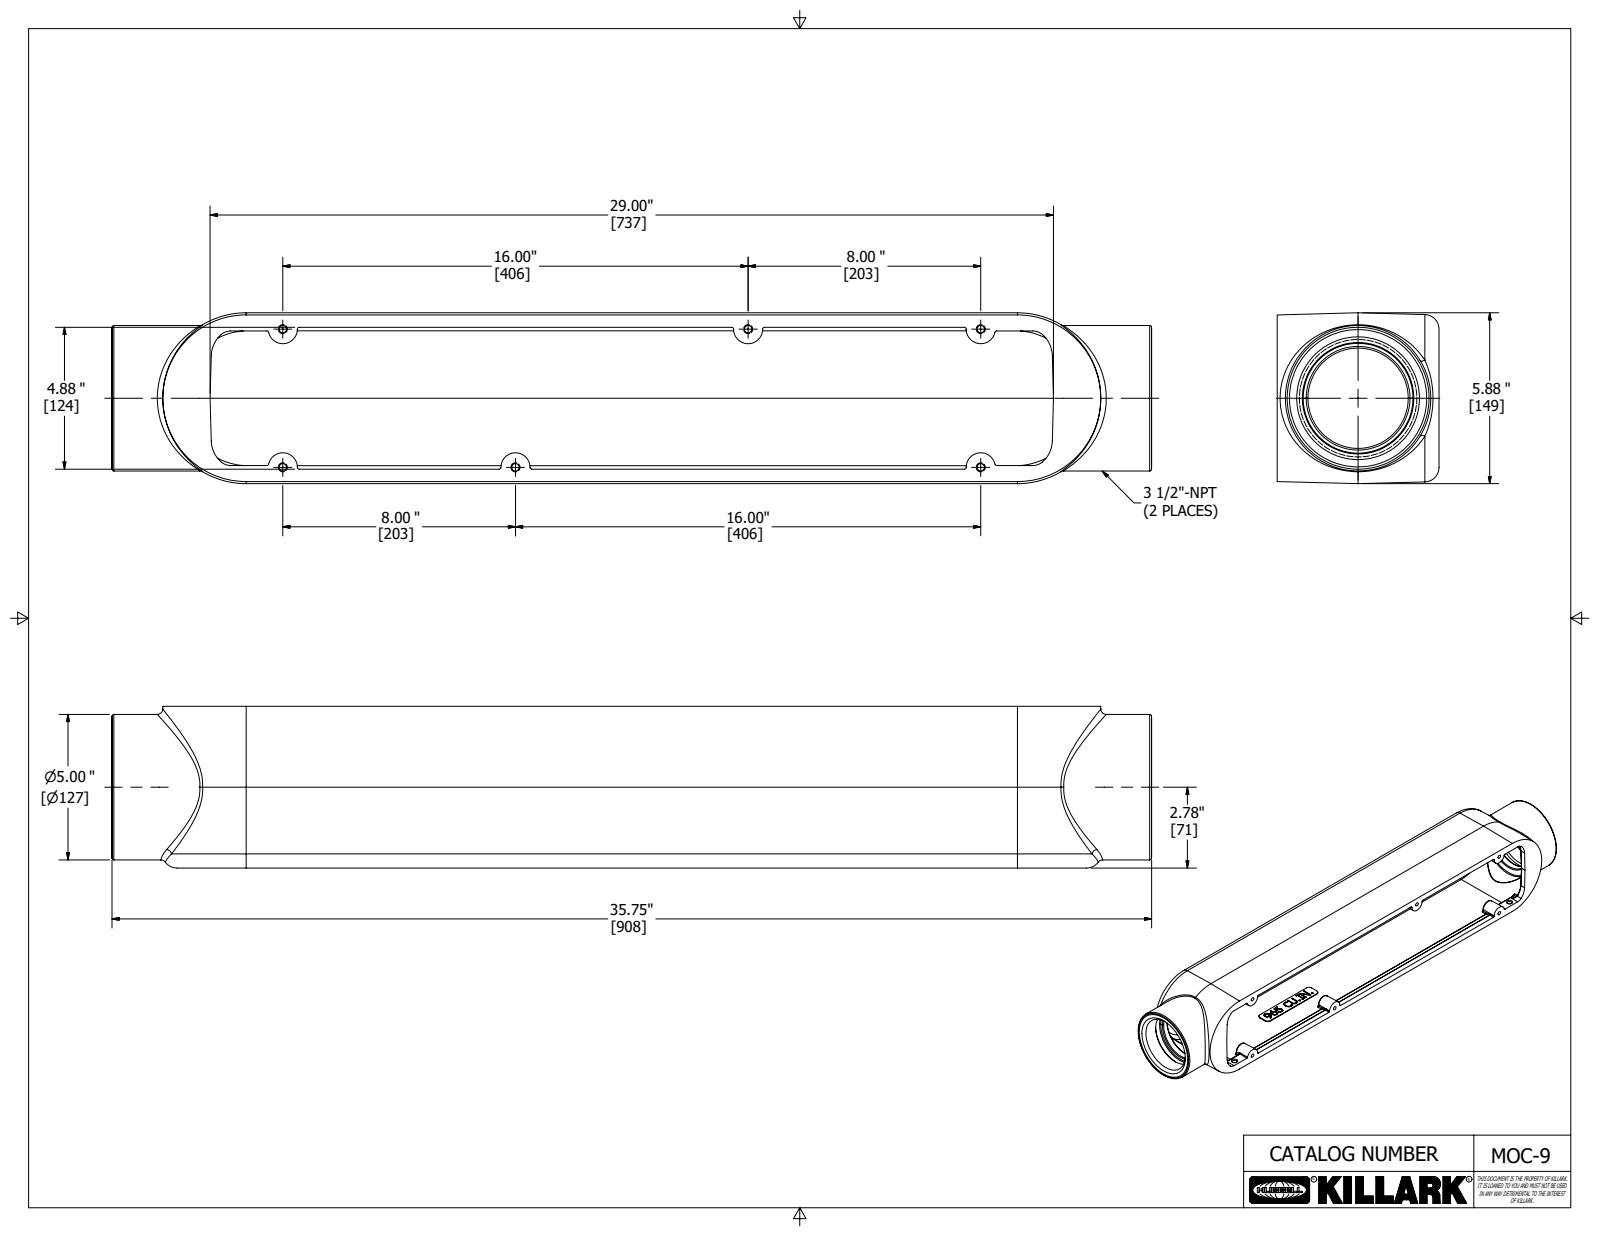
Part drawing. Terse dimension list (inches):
name: 21250-2
written by: Autodesk Inventor 2020 (AUTOMOTIVE_DESIGN)
unit: in
bodies: 1 solid, 744 faces (267 planar, 106 cylindrical, 371 other)
size: 35.75 × 5.875 × 5.563
volume: 230.3 in³; area: 1 217 in²
holes: 6× ⌀0.252, 1× ⌀3.448, 1× ⌀4.011, 1× ⌀4.5
bosses: 1× ⌀5
rounds: 60× R0.062, 6× R0.5, 4× R1, 2× R0.063, 2× R0.125, 2× R0.25, 2× R2.562
face distances: 5.875, 5.125, 5.562, 0.125, 5, 0.031, 5.531, 4.875, 4.812, 31.5
hole spacings: 9.304, 4.75, 8, 16, 16.69, 24, 24.465
